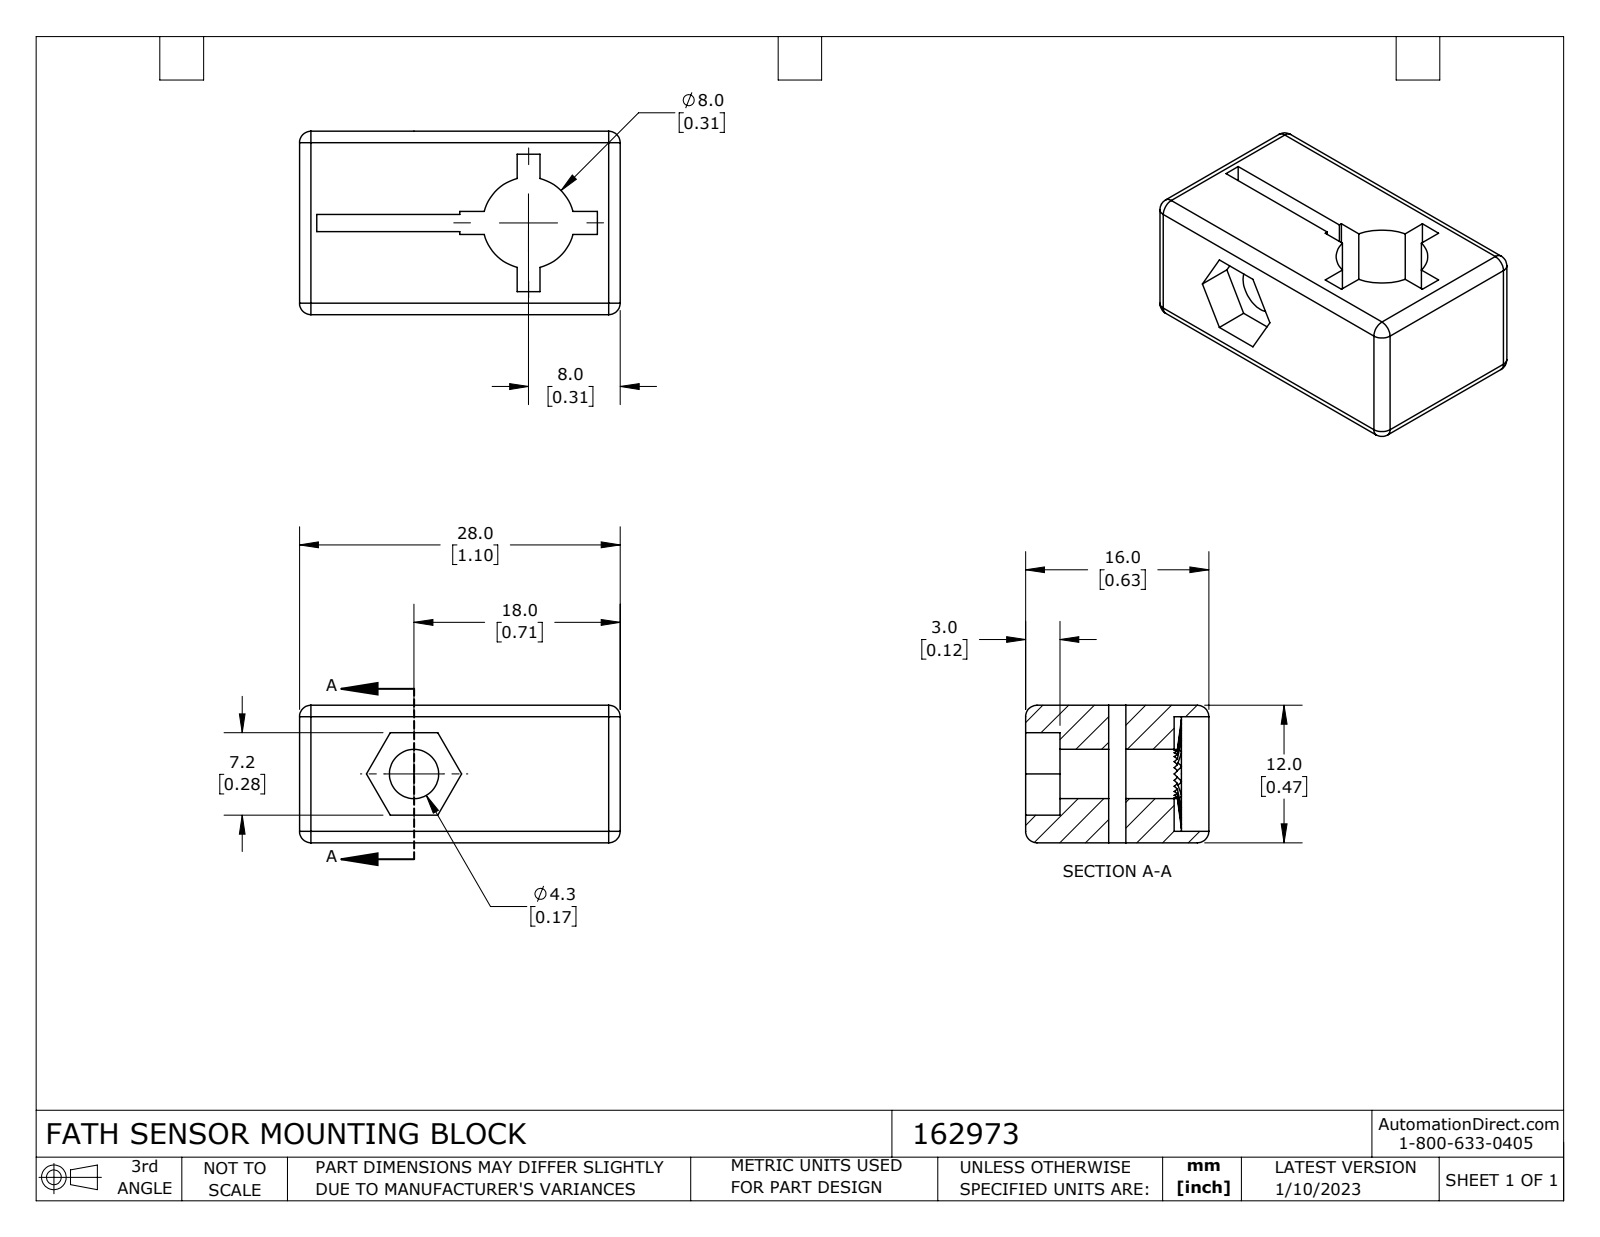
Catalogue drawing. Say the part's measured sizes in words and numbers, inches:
The part is named "162973". Its 3-D file was written by "SolidWorks 2021 (CONFIG_CONTROL_DESIGN)". It is 1 solid with 204 faces: 174 planar, 22 cylindrical and 8 other. Overall it measures 1.102 by 0.63 by 0.472 inches. Its volume is 0.233 cubic inches and its surface area 4.238 square inches. Round holes: 1 of diameter 0.169, 1 of diameter 0.394. Partial cylindrical surfaces (rounded edges, fillets, slot ends): 12 of radius 0.039, 1 of radius 0.157. The main face-to-face distances are 0.472, 0.285, 0.344, 0.276, 0.63, 0.079, 0.354, 0.059, 1.102, 0.069.
